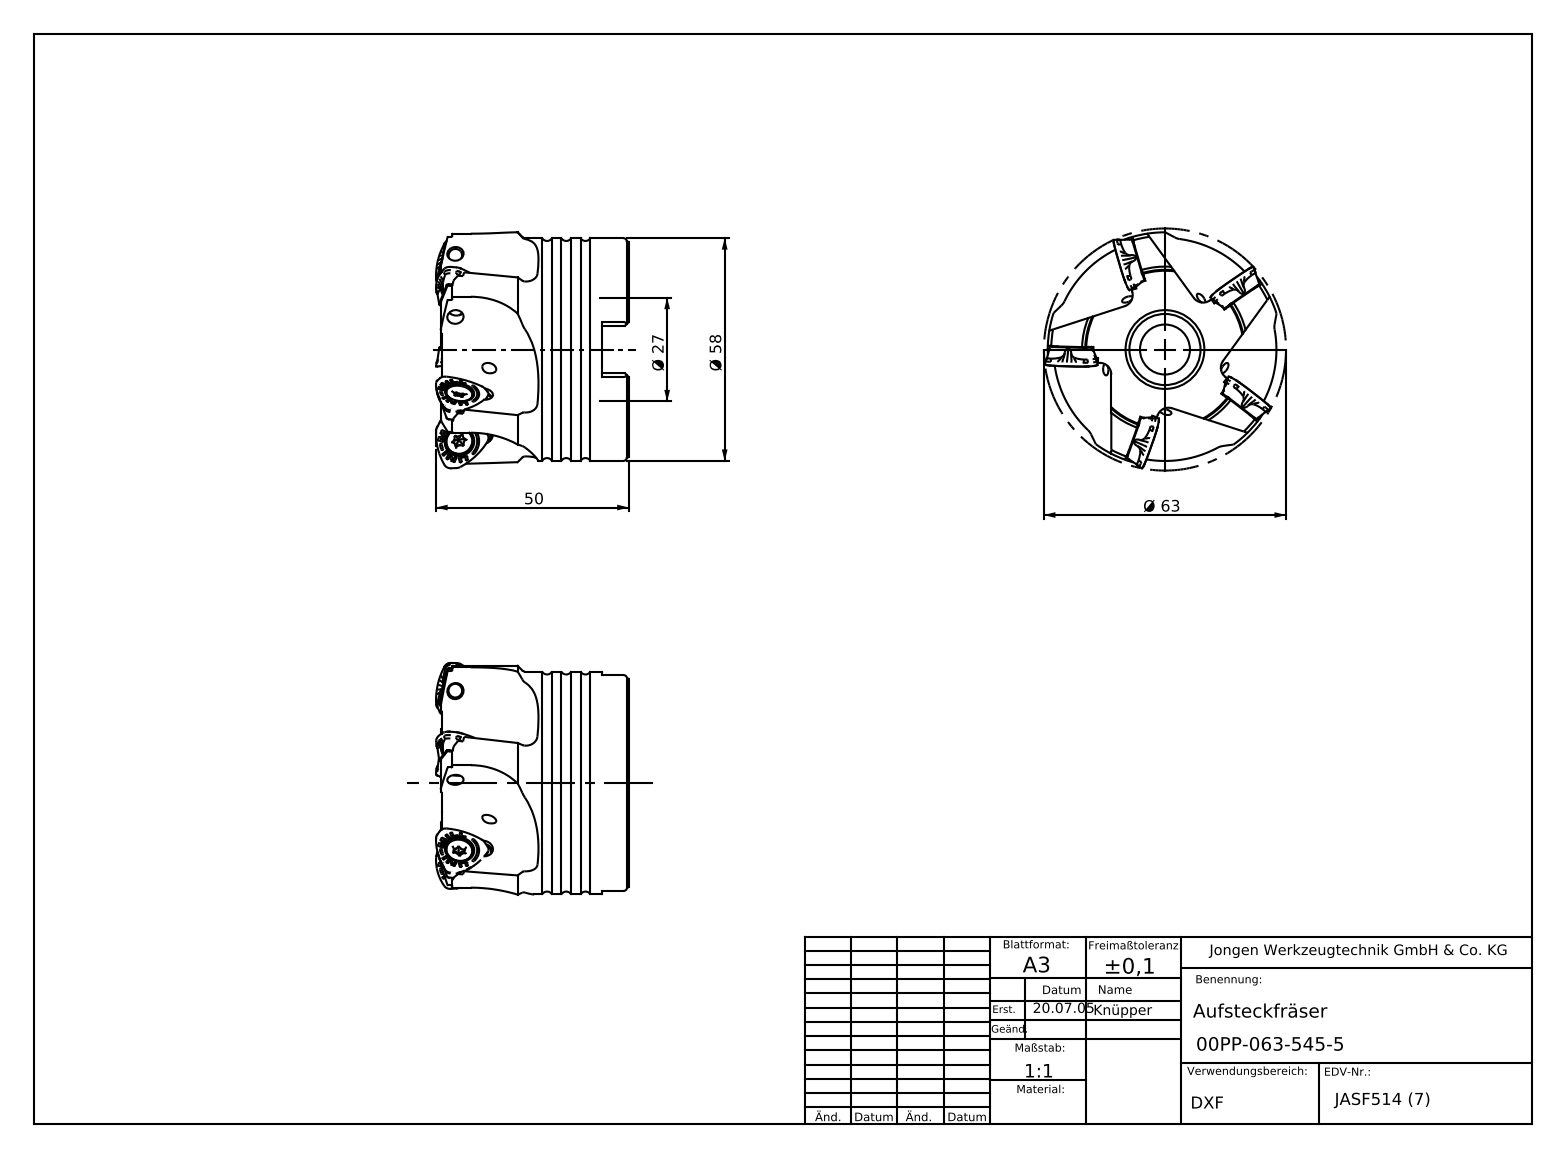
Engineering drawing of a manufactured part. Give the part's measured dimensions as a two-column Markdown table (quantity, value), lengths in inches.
| quantity | value |
| --- | --- |
| part name | 00PP-063-545-5 |
| STEP written by | SolidWorks 2012 (AUTOMOTIVE_DESIGN) |
| units | inches |
| bodies | 1 solid, 229 faces (86 planar, 75 cylindrical, 68 other) |
| overall size | 2.48 × 2.48 × 1.969 |
| volume | 5.959 in³ |
| surface area | 34.05 in² |
| round holes (diameter × count) | 0.118 × 5, 0.512 × 1, 0.728 × 1, 1.055 × 1, 1.063 × 1, 1.069 × 1, 1.075 × 1 |
| round bosses / shafts (diameter × count) | 2.283 × 1 |
| partial cylindrical surfaces (radius × count) | 0.059 × 10, 0.098 × 5, 0.118 × 5, 0.828 × 5, 1.201 × 1 |
| main face-to-face distances | 1.915, 0.274, 1.642, 0.488, 1.376, 1.102, 0.539, 0.051, 0.306, 0.794 |
